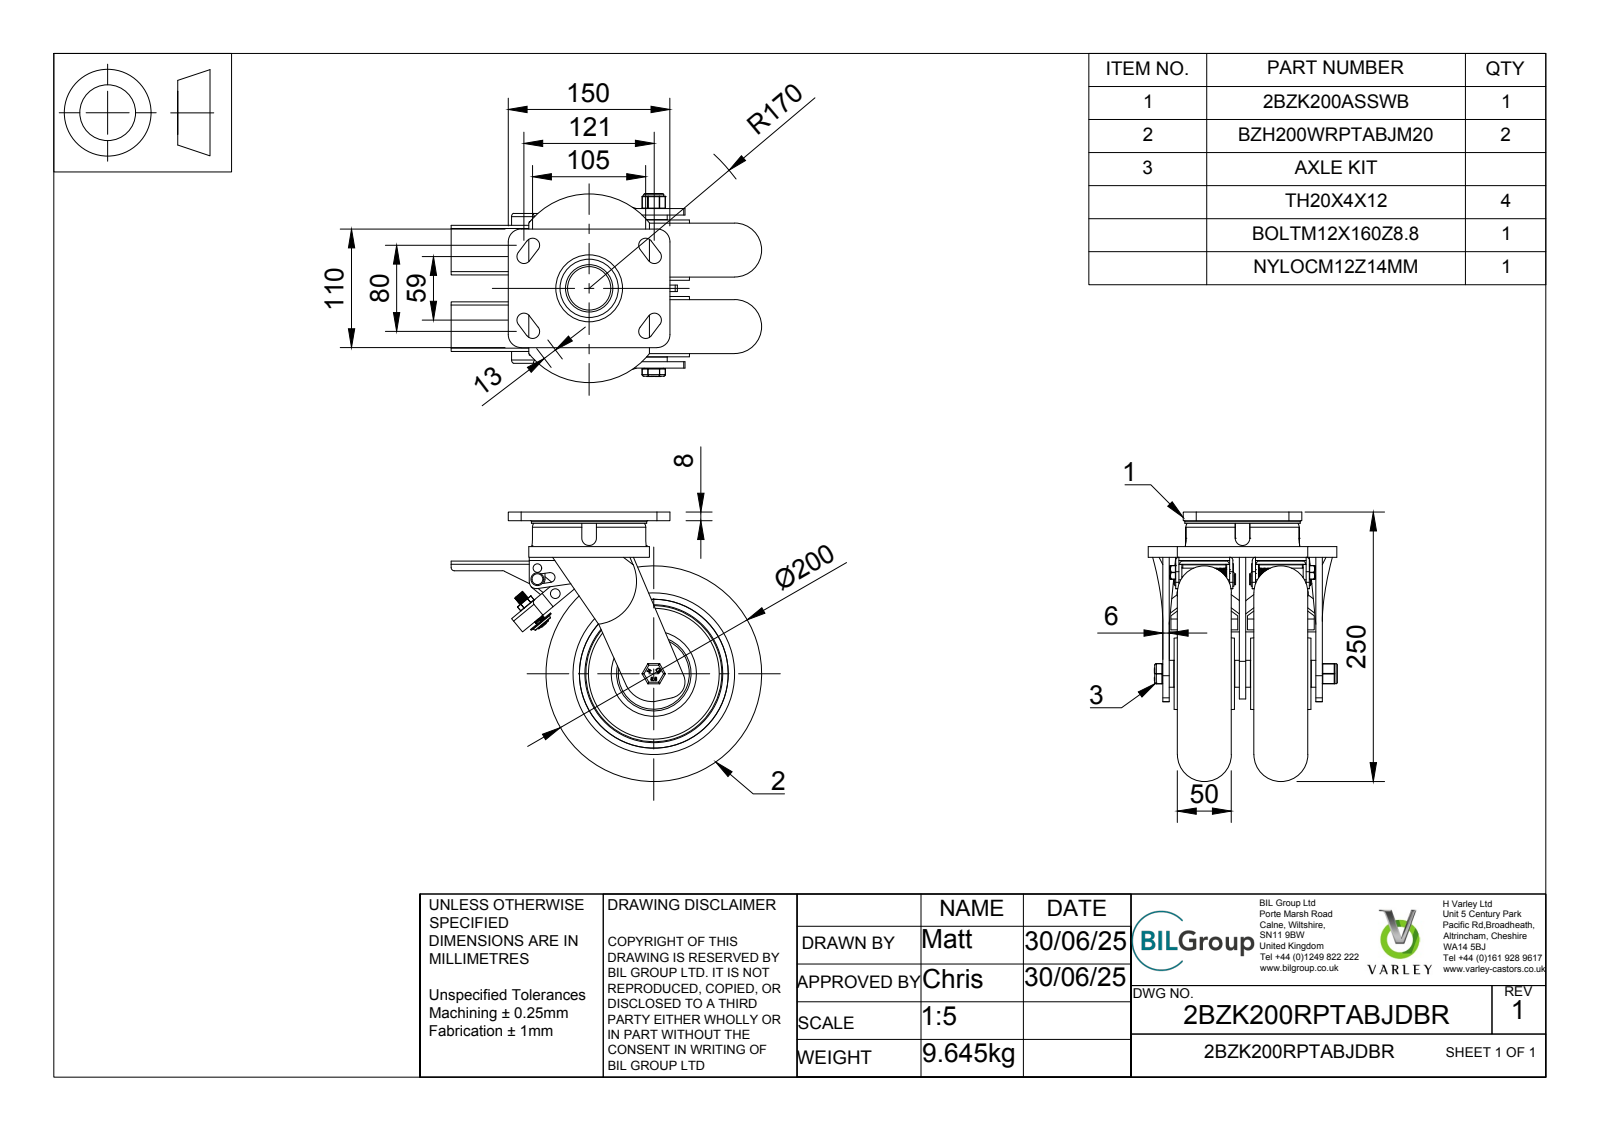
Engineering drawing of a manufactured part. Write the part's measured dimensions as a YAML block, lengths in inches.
part_name: "2BZK200RPTABJDBR v4; 2BZK200ASDBR v1; FABRICATED STEEL TOP PLATE; FABRICATED STEEL FORKS (+1 more)"
step_written_by: "Autodesk Translation Framework v14.10.0.0 (AUTOMOTIVE_DESIGN)"
units: inches
bodies: {solids: 91, faces: 2676, planar: 1043, cylindrical: 648, other: 985}
overall_size: [11.339, 9.843, 6.909]
volume: 174.6
surface_area: 1083
round_holes:
  - {diameter: 0.354, count: 12}
  - {diameter: 0.236, count: 3}
  - {diameter: 0.551, count: 3}
  - {diameter: 0.157, count: 2}
  - {diameter: 0.394, count: 2}
  - {diameter: 0.118, count: 1}
  - {diameter: 0.315, count: 1}
  - {diameter: 0.472, count: 1}
  - {diameter: 0.492, count: 1}
  - {diameter: 0.496, count: 1}
  - {diameter: 0.787, count: 1}
  - {diameter: 1.122, count: 1}
round_bosses_or_shafts:
  - {diameter: 0.354, count: 12}
  - {diameter: 0.315, count: 4}
  - {diameter: 0.945, count: 3}
  - {diameter: 0.472, count: 3}
  - {diameter: 0.709, count: 2}
  - {diameter: 4.213, count: 1}
  - {diameter: 4.173, count: 1}
  - {diameter: 1.606, count: 1}
partial_cylinders:
  - {radius: 0.01, count: 54}
  - {radius: 0.02, count: 18}
  - {radius: 0.118, count: 18}
  - {radius: 0.256, count: 8}
  - {radius: 0.059, count: 6}
  - {radius: 0.266, count: 6}
  - {radius: 0.591, count: 5}
  - {radius: 0.019, count: 4}
face_to_face_distances: [2.795, 1.398, 0.236, 0.138, 1.26, 1.772, 0.374, 0.531, 0.118, 1.535]
hole_center_spacings: [3.012, 1.559, 4.259, 5.819, 5.217, 5.217, 6.024, 6.024]
